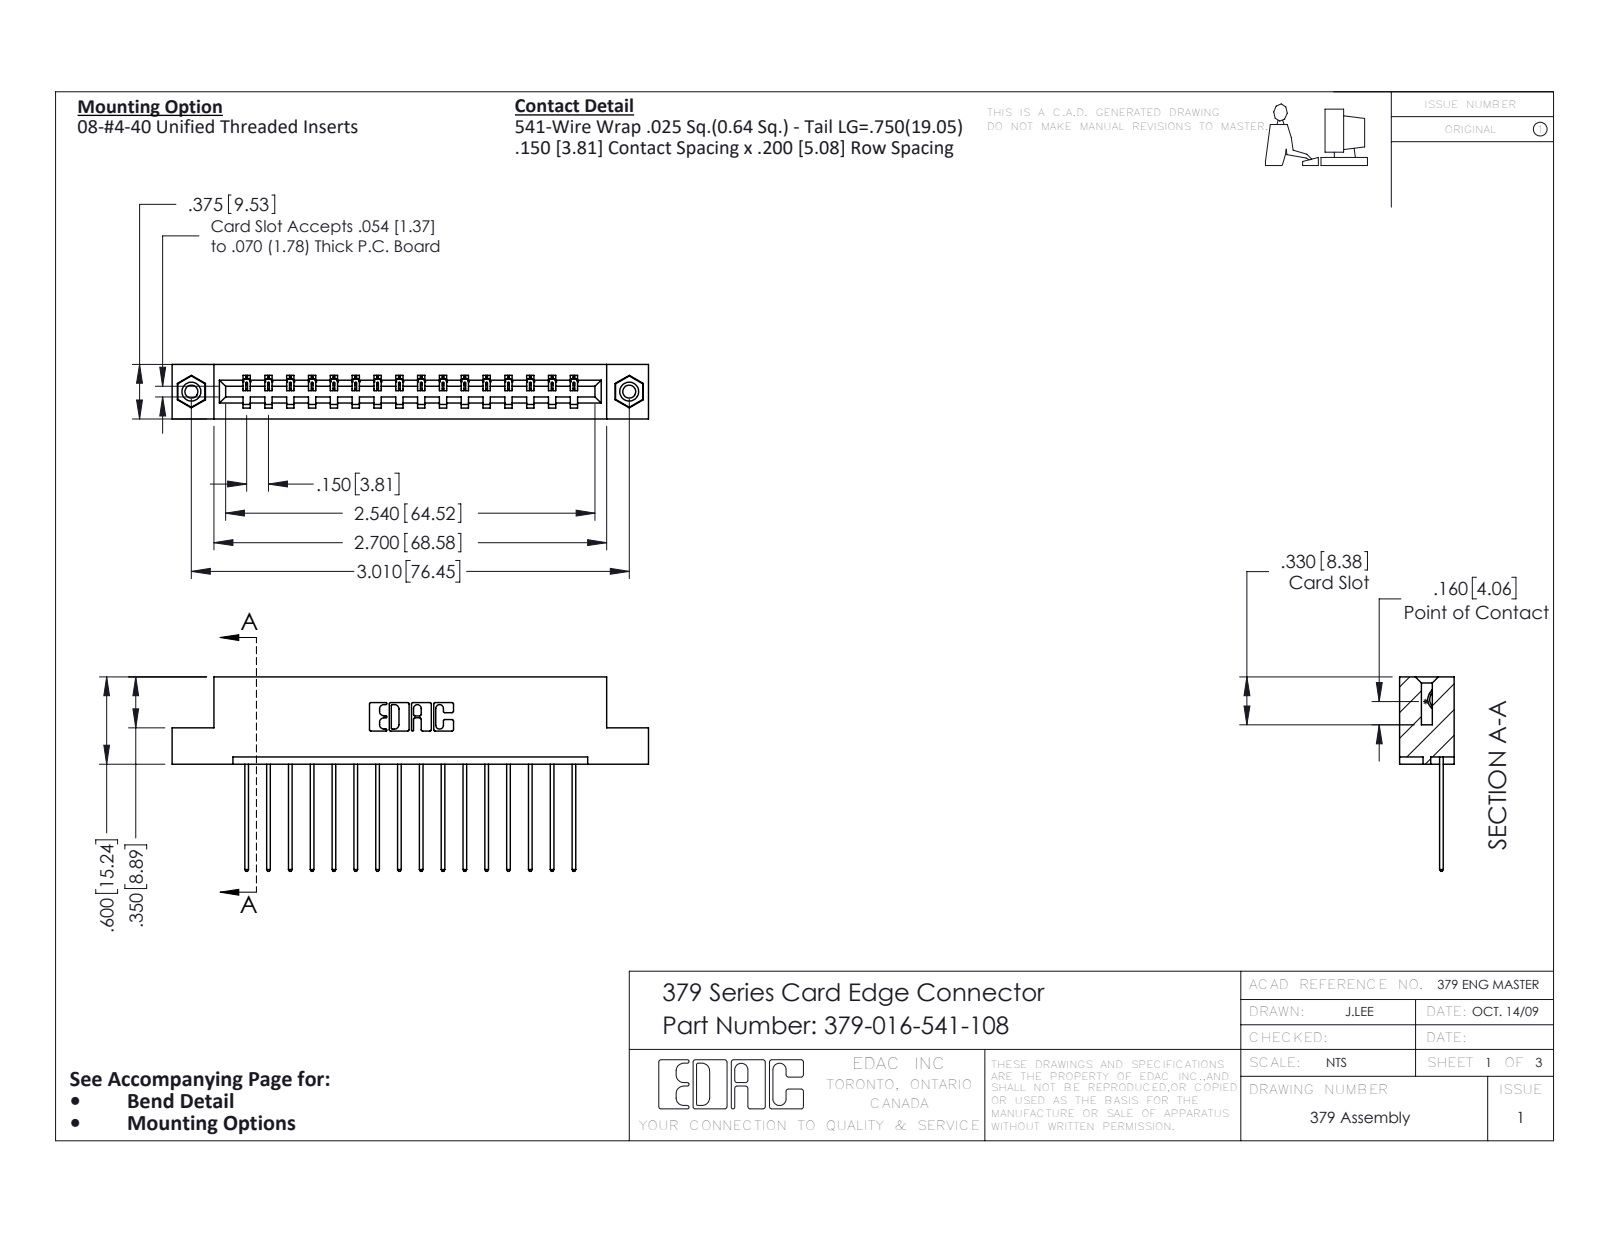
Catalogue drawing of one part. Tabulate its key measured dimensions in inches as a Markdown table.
| quantity | value |
| --- | --- |
| part name | 379-016-541-108; 345-250-001_345-250-003-102; 345-292-001_345-293-141; 379 Part_Flush - .156 Dia - TI |
| STEP written by | SolidWorks 2020 (CONFIG_CONTROL_DESIGN) |
| units | inches |
| bodies | 19 solids, 1102 faces (774 planar, 312 cylindrical, 16 other) |
| overall size | 3.275 × 1.337 × 0.375 |
| volume | 0.517 in³ |
| surface area | 13.79 in² |
| round holes (diameter × count) | 0.089 × 2, 0.125 × 2, 0.156 × 2 |
| round bosses / shafts (diameter × count) | 0.155 × 2 |
| partial cylindrical surfaces (radius × count) | 0.006 × 32, 0.01 × 32, 0.01 × 22, 0.007 × 6, 0.031 × 6, 0.026 × 3, 0.014 × 1, 0.022 × 1 |
| main face-to-face distances | 0.3, 0.075, 0.375, 0.6, 0.15, 0.225, 0.45, 0.2, 0.275, 0.1 |
| hole center spacings | 3.01 |
